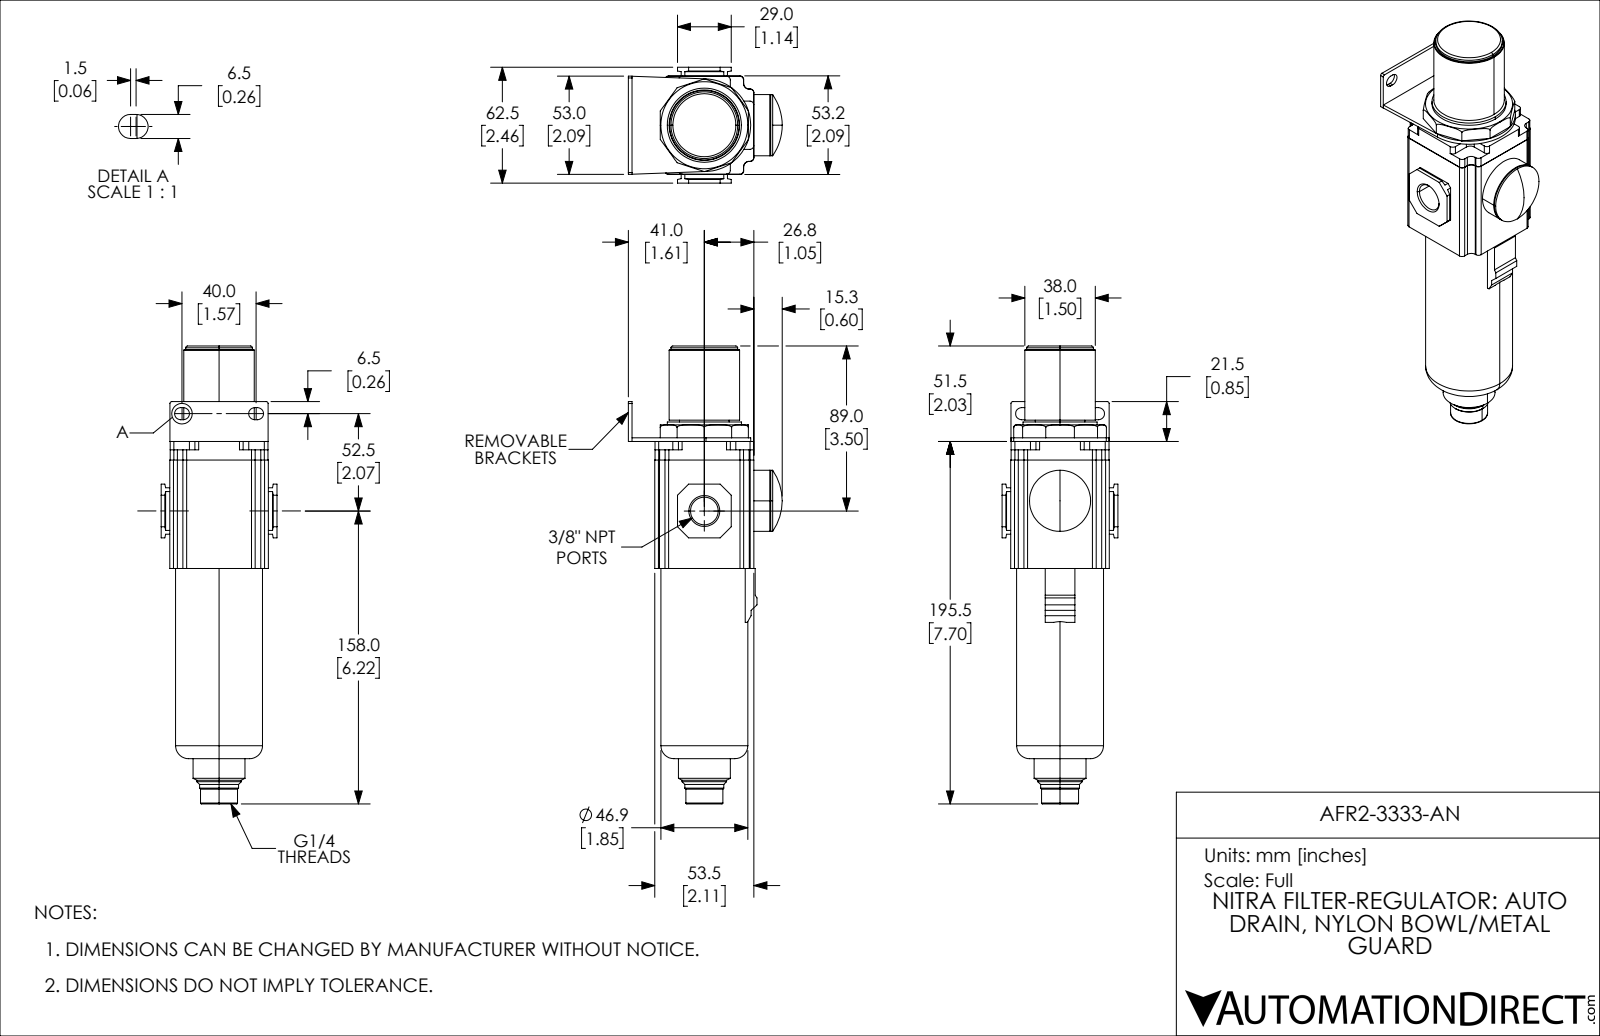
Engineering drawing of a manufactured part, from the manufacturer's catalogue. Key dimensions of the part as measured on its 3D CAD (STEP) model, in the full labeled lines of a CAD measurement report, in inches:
Part name (STEP PRODUCT): AFR2-3333-AN
STEP written by: SolidWorks 2019 (CONFIG_CONTROL_DESIGN)
Units: inches
Bodies: 1 solid, 221 faces (124 planar, 71 cylindrical, 26 other)
Overall size (bounding box): 9.724 × 3.269 × 2.461
Volume: 27.43 in³ · Surface area: 80.97 in²
Round holes (diameter × count): ⌀0.451 ×1, ⌀0.589 ×1
Round bosses / shafts (diameter × count): ⌀1.846 ×1, ⌀1.575 ×1, ⌀1.496 ×1, ⌀1.417 ×1, ⌀1.299 ×1, ⌀1.102 ×1, ⌀1.054 ×1, ⌀0.945 ×1
Partial cylindrical surfaces — rounded edges, fillets, slot ends (radius × count): R0.079 ×24, R0.118 ×12, R0.128 ×4, R0.039 ×2, R0.984 ×1
Main face-to-face distances: 0.079, 2.094, 2.106, 0.561, 0.183, 2.278, 0.482, 2.667, 2.028, 1.949
